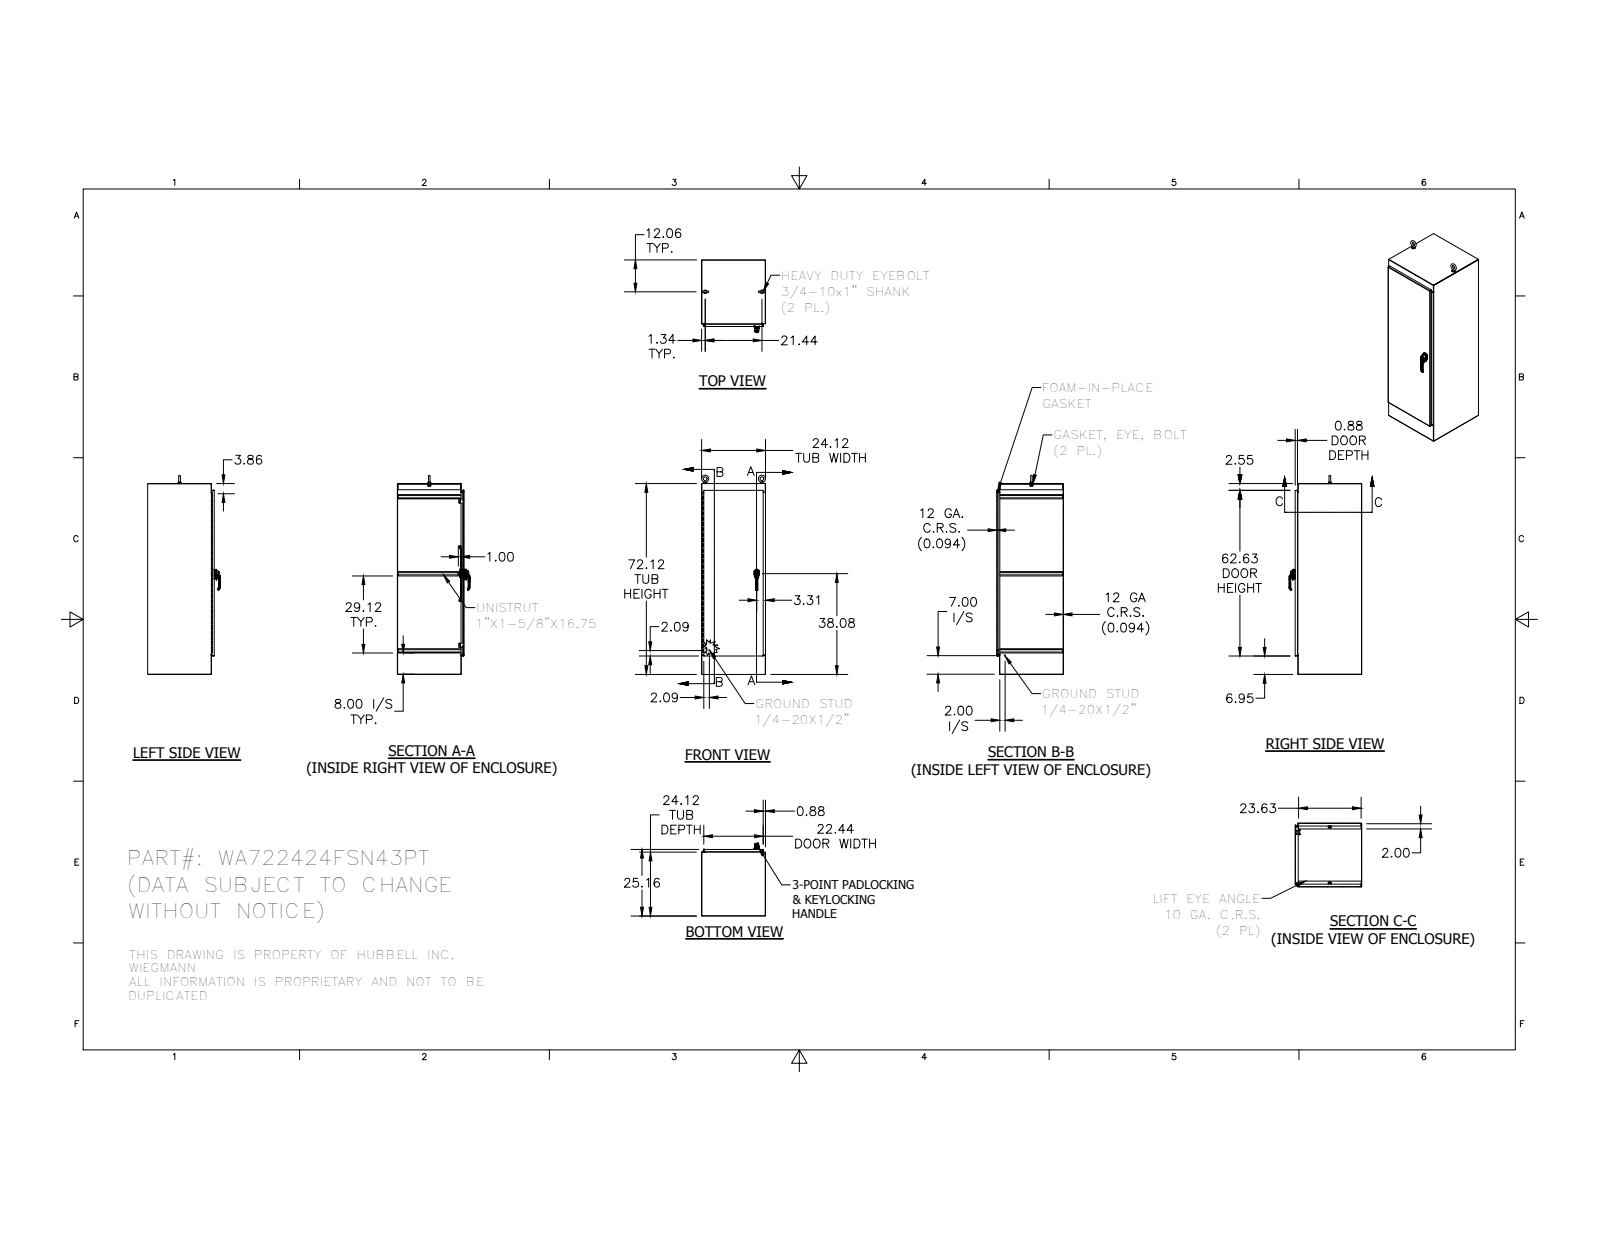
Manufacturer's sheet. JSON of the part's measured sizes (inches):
{"part_name": "HSSN1300W60T; 38846; 37029; FUN00103-22.75 (+8 more)", "step_written_by": "SolidWorks 2014 (AUTOMOTIVE_DESIGN)", "units": "inches", "bodies": {"solids": 52, "faces": 1938, "planar": 834, "cylindrical": 782, "other": 322}, "overall_size": [75.248, 25.16, 24.125], "volume_in3": 945.2, "surface_area_in2": 19514, "round_holes": [[0.277, 8], [0.2, 4], [0.28, 3], [0.241, 2], [0.25, 2], [0.252, 2], [0.4, 2], [0.407, 2], [0.45, 2], [0.642, 2], [0.813, 2], [0.125, 1]], "round_bosses_or_shafts": [[0.25, 3], [1.25, 2], [1.12, 2], [1, 2], [0.75, 2], [0.563, 2], [0.527, 2], [0.5, 2]], "partial_cylinders_radius": [[0.01, 16], [0.031, 16], [0.05, 14], [0.125, 14], [0.019, 12], [0.053, 12], [0.086, 12], [0.125, 12]], "face_to_face_distances": [0.094, 24.031, 25.067, 23.938, 24.125, 24.973, 25.161, 72.031, 1.035, 71.938], "hole_center_spacings": [54.196, 54.946, 0.762, 0.764, 1.195, 1.271, 54.561, 54.571]}
